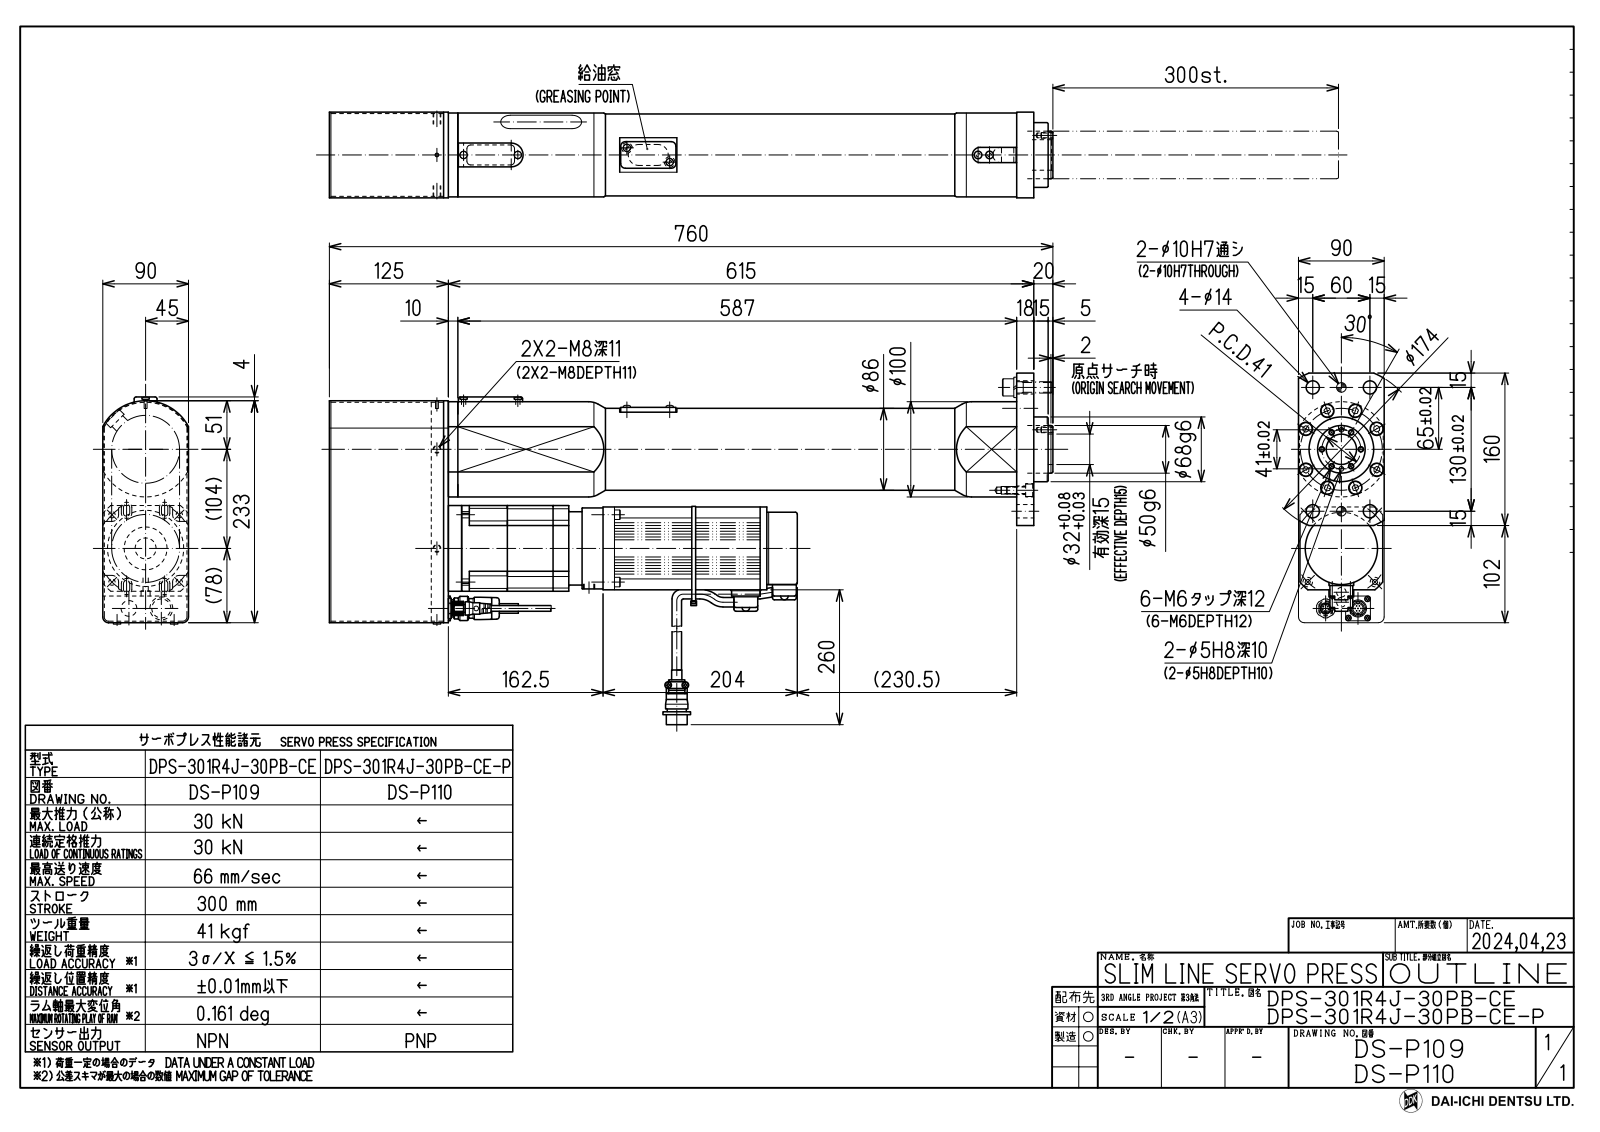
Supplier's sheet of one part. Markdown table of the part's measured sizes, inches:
| quantity | value |
| --- | --- |
| part name | DPS-301R4J-30PB-CE(-P)(DS-P109_P110)_OUTLINE; DPS-301R4J-30PB-CE(DS-P109)_BODY; DPS-301R4J-30FB-CE_(DS-P072)_可動部 |
| STEP written by | Autodesk Inventor 2023 (CONFIG_CONTROL_DESIGN) |
| units | inches |
| bodies | 2 solids, 1683 faces (984 planar, 403 cylindrical, 296 other) |
| overall size | 29.921 × 10.374 × 3.543 |
| volume | 553.6 in³ |
| surface area | 1 029 in² |
| round holes (diameter × count) | 0.194 × 12, 0.551 × 12, 0.126 × 4, 0.315 × 4, 0.047 × 3, 0.197 × 2, 0.262 × 2, 0.394 × 2, 0.097 × 1, 0.122 × 1, 0.128 × 1, 0.157 × 1 |
| round bosses / shafts (diameter × count) | 0.512 × 8, 0.315 × 8, 0.039 × 7, 0.276 × 6, 0.118 × 6, 0.394 × 4, 0.335 × 4, 0.295 × 4 |
| partial cylindrical surfaces (radius × count) | 0.024 × 48, 0.039 × 27, 0.118 × 14, 0.012 × 12, 0.079 × 12, 0.197 × 10, 0.059 × 8, 0.128 × 8 |
| main face-to-face distances | 0.059, 3.543, 3.484, 0.039, 0.118, 3.504, 0.65, 0.177, 0.236, 0.709 |
| hole center spacings | 1.693, 3.182, 0.557, 0.582, 0.787, 1.128, 1.14, 1.158 |
